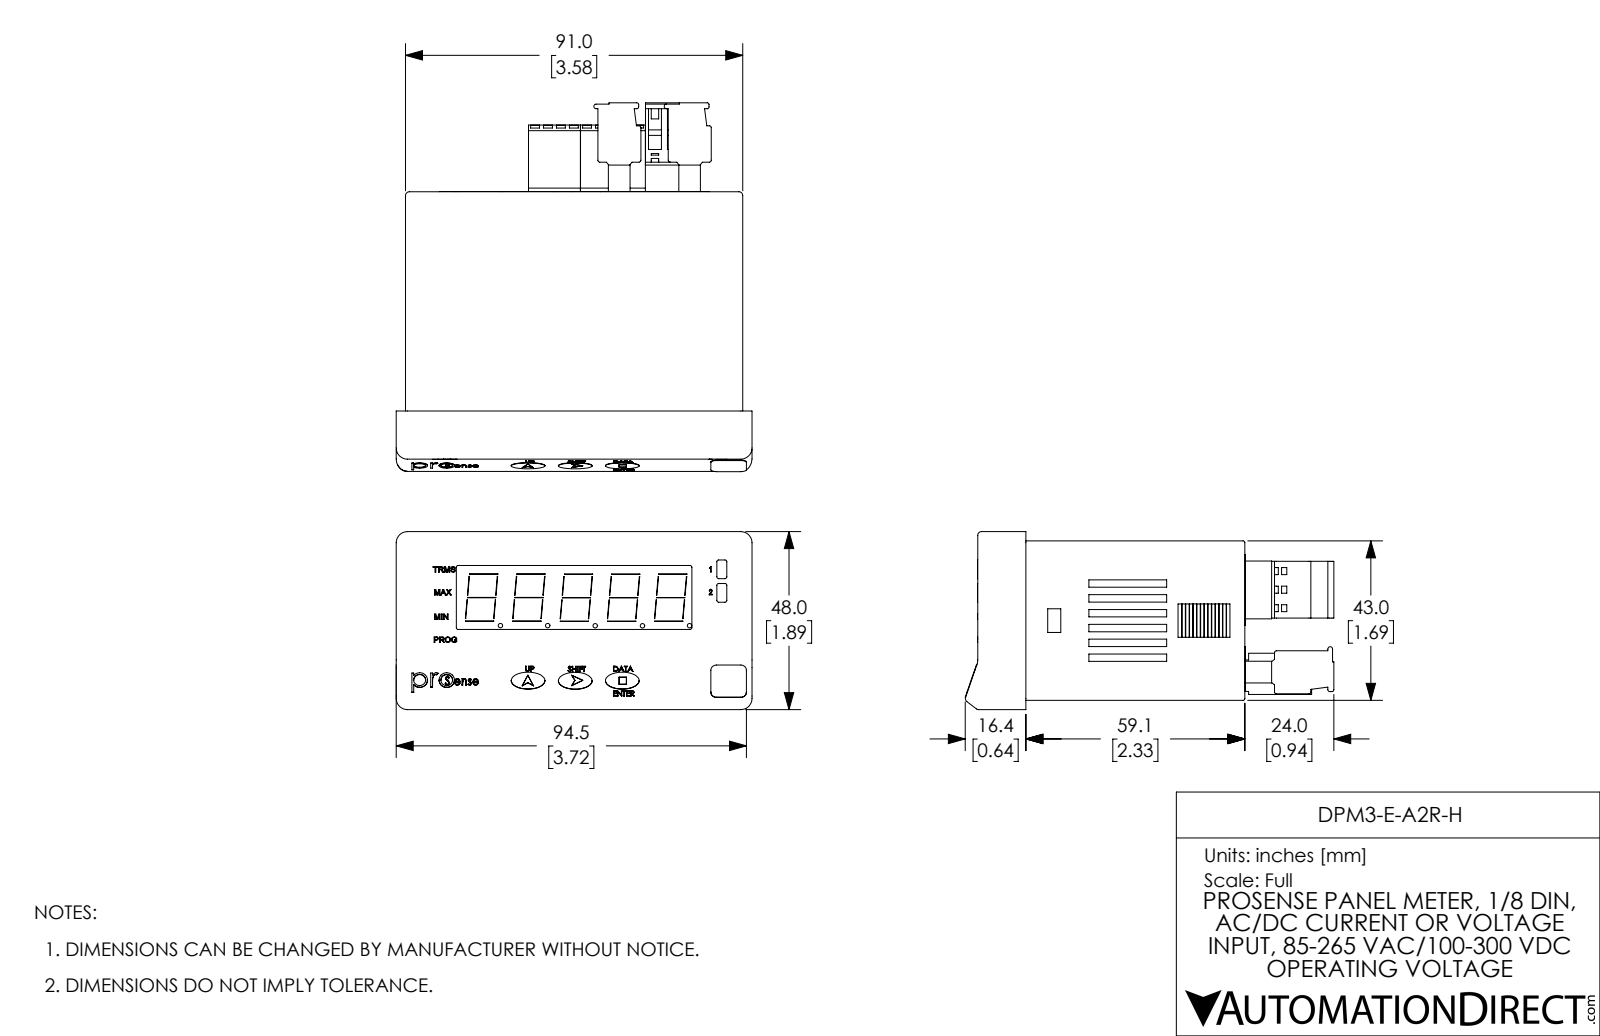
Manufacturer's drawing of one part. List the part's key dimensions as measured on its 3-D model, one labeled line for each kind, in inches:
Part name (STEP PRODUCT): DPM3-E-H B1 Coord a
STEP written by: SolidWorks 2017 (AUTOMOTIVE_DESIGN)
Units: inches
Bodies: 10 solids, 2235 faces (1701 planar, 303 cylindrical, 231 other)
Overall size (bounding box): 3.916 × 3.78 × 1.89
Volume: 5.391 in³ · Surface area: 99.83 in²
Round holes (diameter × count): ⌀0.039 ×9, ⌀0.079 ×9, ⌀0.078 ×8, ⌀0.118 ×8, ⌀0.152 ×8
Round bosses / shafts (diameter × count): ⌀0.047 ×5
Partial cylindrical surfaces — rounded edges, fillets, slot ends (radius × count): R0.004 ×53, R0.02 ×29, R0.012 ×18, R0.014 ×18, R0.118 ×10, R0.039 ×9, R0.07 ×9, R0.072 ×9
Main face-to-face distances: 0.059, 1.634, 0.098, 1.693, 1.575, 1.732, 0.157, 0.433, 3.524, 2.78
Hole centre spacings: 0.197, 0.201, 0.138, 0.748, 0.276, 0.398, 0.553, 0.691
